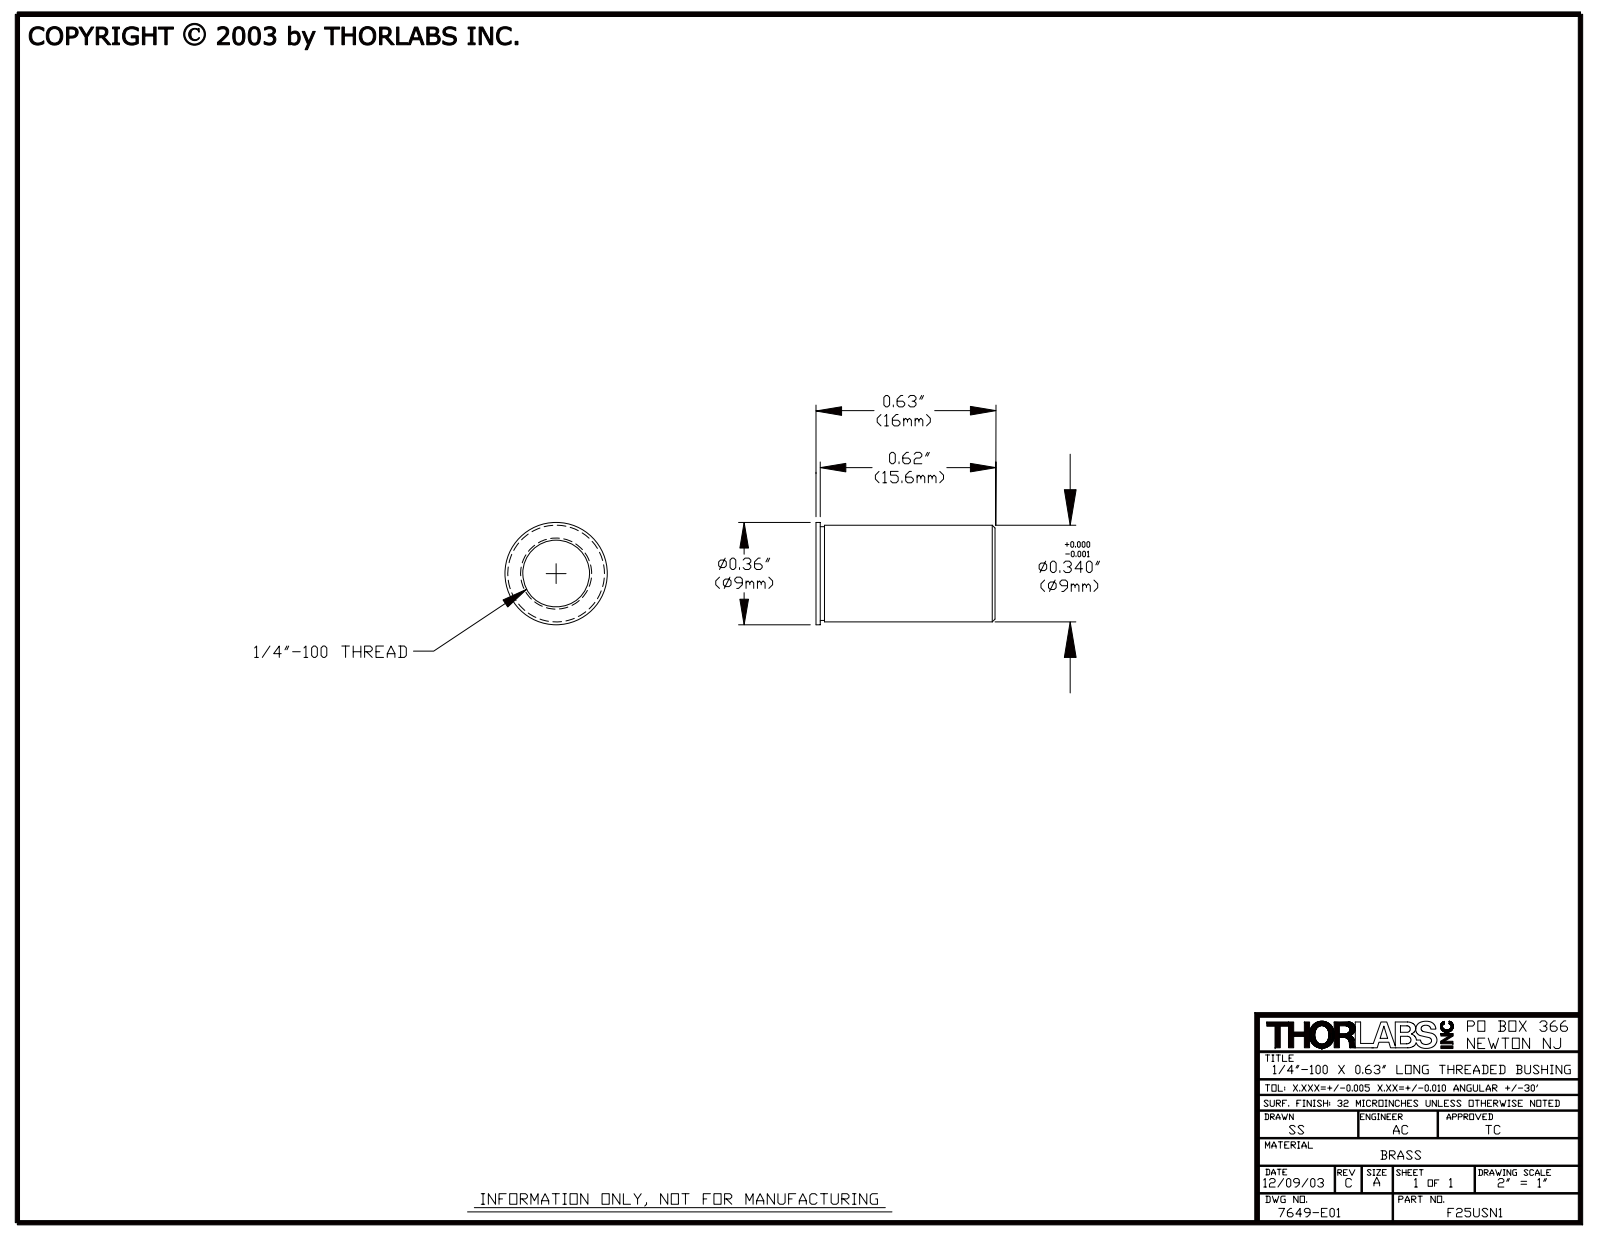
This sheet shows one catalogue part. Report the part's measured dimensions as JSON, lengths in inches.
{"part_name": "7649-E0W", "step_written_by": "SolidWorks 2007 (AUTOMOTIVE_DESIGN)", "units": "inches", "bodies": {"solids": 0, "faces": 219, "planar": 3, "cylindrical": 142, "other": 74}, "overall_size": [0.63, 0.36, 0.36], "round_holes": [[0.235, 1], [0.25, 1]], "round_bosses_or_shafts": [[0.36, 1], [0.34, 1]], "face_to_face_distances": [0.63, 0.015, 0.615]}
